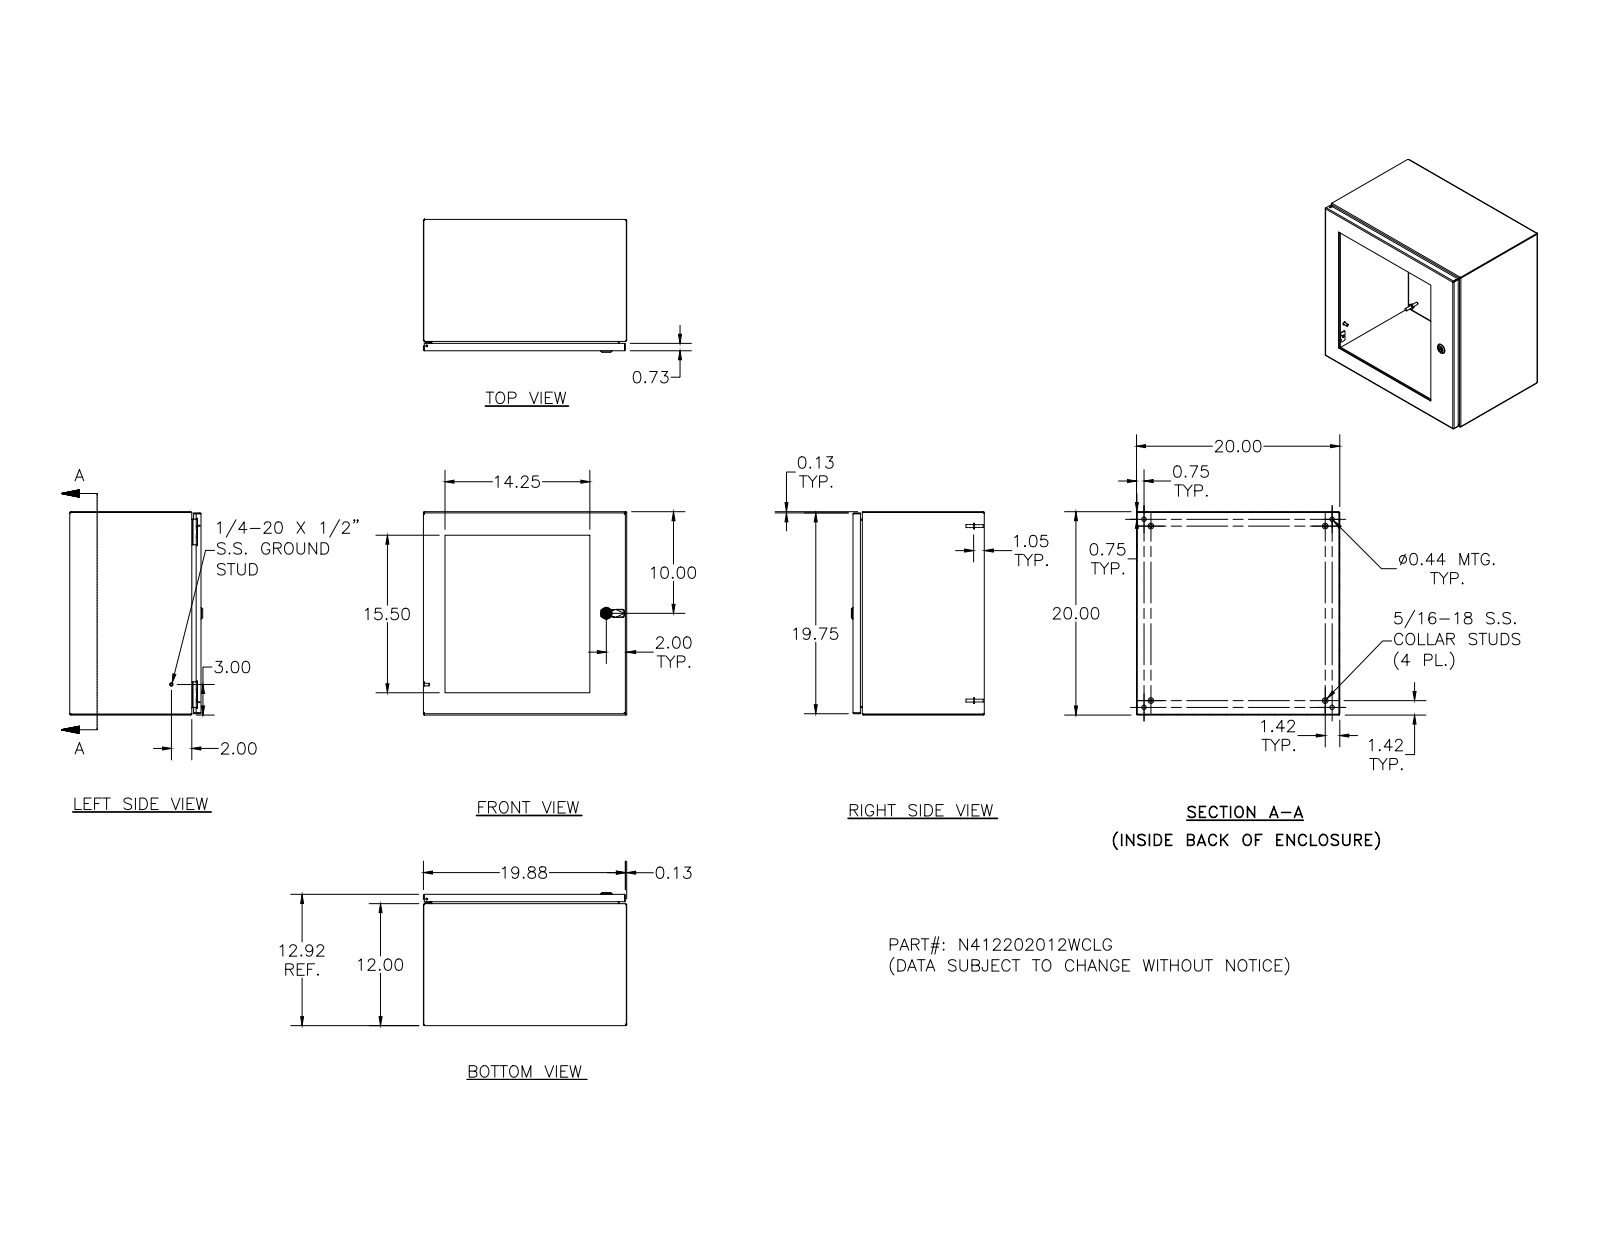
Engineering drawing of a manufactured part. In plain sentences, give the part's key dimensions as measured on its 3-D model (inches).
The part is named "N412202012WCLG". Its 3-D file was written by "SolidWorks 2018 (AUTOMOTIVE_DESIGN)". It is 69 solids with 2019 faces: 753 planar, 617 cylindrical and 649 other. Overall it measures 20 by 20 by 13.075 inches. Its volume is 194.1 cubic inches and its surface area 4 104 square inches. Round holes: 18 of diameter 0.156, 16 of diameter 0.281, 5 of diameter 0.188, 4 of diameter 0.093, 4 of diameter 0.152, 4 of diameter 0.167, 4 of diameter 0.172, 4 of diameter 0.437, 1 of diameter 0.187, 1 of diameter 0.197, 1 of diameter 0.315, 1 of diameter 0.394. Round bosses or shafts: 16 of diameter 0.337, 16 of diameter 0.19, 10 of diameter 0.25, 4 of diameter 0.563, 4 of diameter 0.36, 4 of diameter 0.32, 4 of diameter 0.3, 4 of diameter 0.275. Partial cylindrical surfaces (rounded edges, fillets, slot ends): 34 of radius 0.031, 30 of radius 0.012, 26 of radius 0.05, 24 of radius 0.105, 18 of radius 0.016, 16 of radius 0.125, 13 of radius 0.02, 8 of radius 0.032. The main face-to-face distances are 0.074, 19.926, 12.843, 20, 19.852, 12.769, 0.25, 12.593, 12.519, 12.917. The hole center spacings are 4, 8, 16.008, 16, 17.221, 6.221, 8.585, 10.035.
